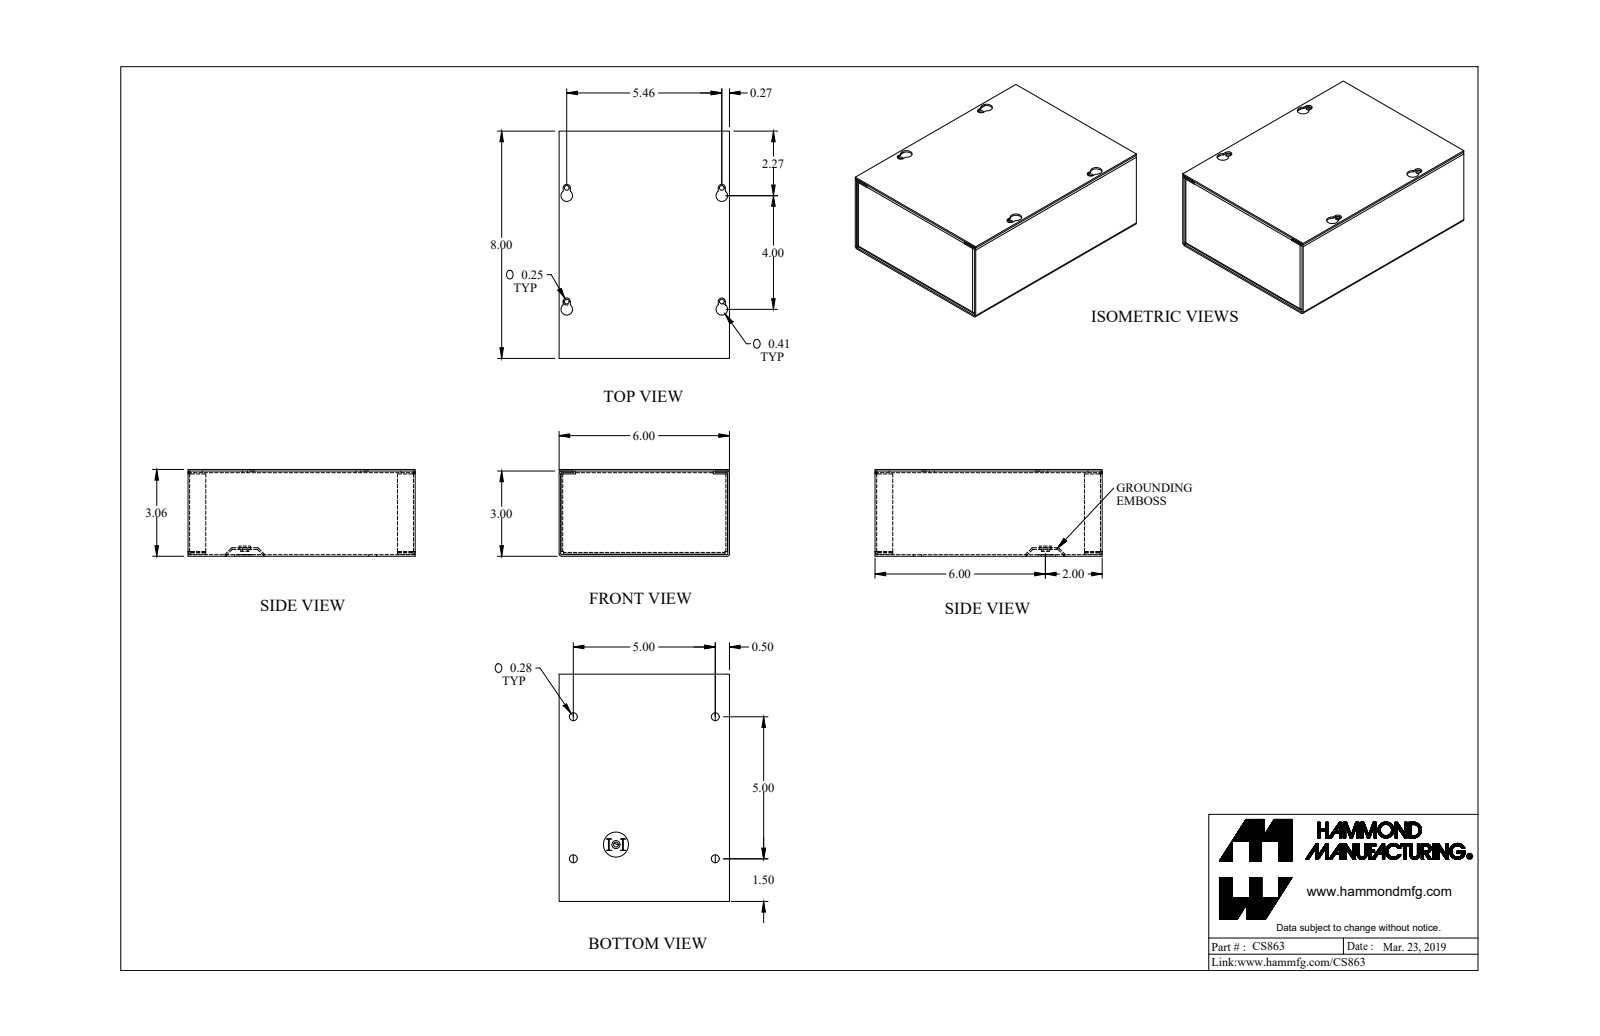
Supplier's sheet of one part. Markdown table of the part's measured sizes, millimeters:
| quantity | value |
| --- | --- |
| part name | CS863_Default |
| STEP written by | SolidWorks 2019 (CONFIG_CONTROL_DESIGN) |
| units | millimeters |
| bodies | 4 solids, 205 faces (125 planar, 72 cylindrical, 8 other) |
| overall size | 203.2 × 152.4 × 77.6 |
| volume | 185 800 mm³ |
| surface area | 261 400 mm² |
| round holes (diameter × count) | 4.3 × 5, 7.1 × 4, 12.7 × 1 |
| round bosses / shafts (diameter × count) | 12.5 × 1, 7.2 × 1 |
| partial cylindrical surfaces (radius × count) | 0.7 × 12, 2.2 × 12, 1.4 × 8, 3.2 × 4, 5.2 × 4 |
| main face-to-face distances | 1.4, 76.2, 74.8, 151, 77.6, 201.8, 152.4, 149.5, 203.2, 200.3 |
| hole center spacings | 14, 114.5, 127, 133.5, 175.3, 101.6, 138.7, 171.9 |
